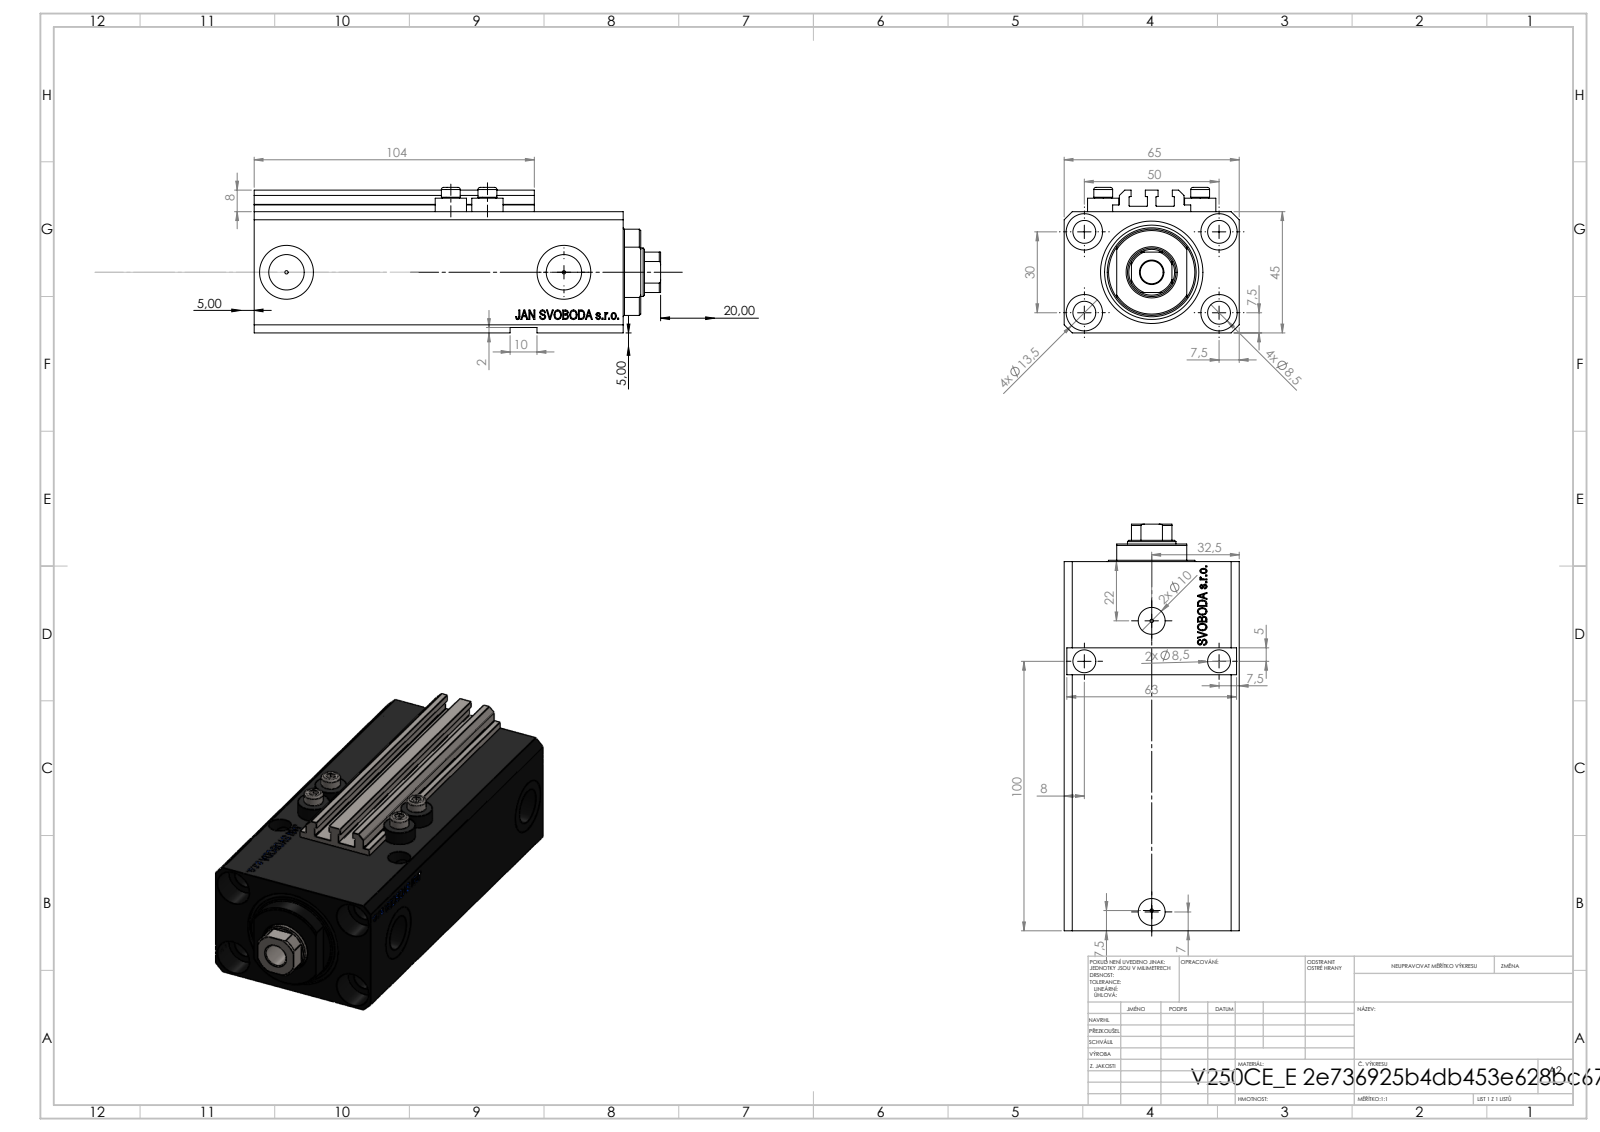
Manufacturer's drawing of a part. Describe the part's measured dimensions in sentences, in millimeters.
The part is named "ALLEN BOLT V250CE; V250CE_VC_E; V250CE_C_VCP; V250CE_E_Body". Its 3-D file was written by "SolidWorks 2019 (CONFIG_CONTROL_DESIGN)". It is 8 solids with 1103 faces: 515 planar, 158 cylindrical and 430 other. Overall it measures 151 by 65 by 54 millimeters. Its volume is 346 877 cubic millimeters and its surface area 94 683 square millimeters. Round holes: 9 of diameter 8.5, 4 of diameter 1.25, 4 of diameter 4, 4 of diameter 13.5, 2 of diameter 10, 2 of diameter 13.16, 2 of diameter 20, 1 of diameter 18, 1 of diameter 25, 1 of diameter 38. Round bosses or shafts: 4 of diameter 11.6, 4 of diameter 7. Partial cylindrical surfaces (rounded edges, fillets, slot ends): 10 of radius 0.2, 1 of radius 8.5, 1 of radius 16. The main face-to-face distances are 45, 65, 47, 2, 123, 2.5, 14, 10, 20.4, 137. The hole center spacings are 29.15, 50, 13.6, 15.12, 27.89, 30, 33.61, 33.62.
